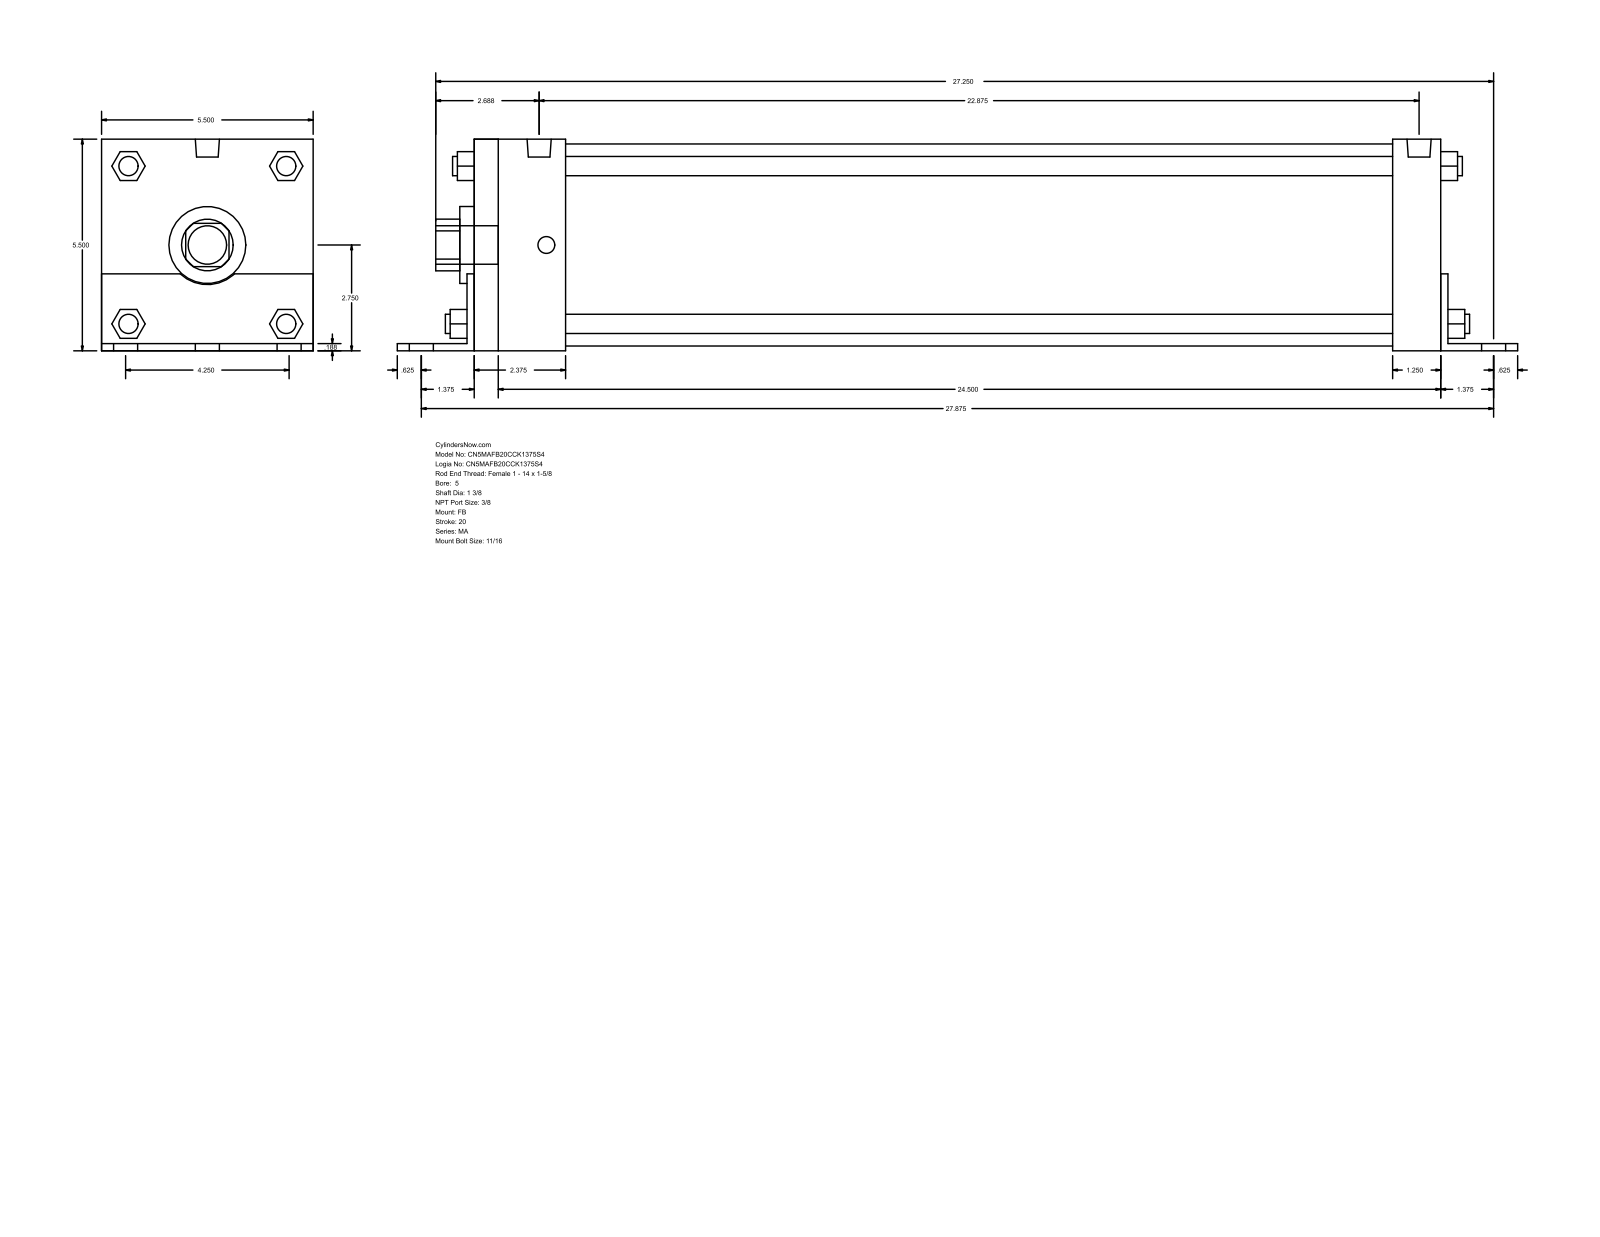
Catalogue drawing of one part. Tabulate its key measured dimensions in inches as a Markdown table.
| quantity | value |
| --- | --- |
| part name | MA_FB__0500_1.375 |
| STEP written by | GSSL Pune (CONFIG_CONTROL_DESIGN) |
| units | inches |
| bodies | 0 solids, 140 faces (105 planar, 35 cylindrical, 0 other) |
| overall size | 29.125 × 5.502 × 5.5 |
| round holes (diameter × count) | 1.375 × 1, 2 × 1, 5.25 × 1 |
| round bosses / shafts (diameter × count) | 0.687 × 6, 0.5 × 4, 0.437 × 4, 0.627 × 2, 1 × 1 |
| partial cylindrical surfaces (radius × count) | 0.672 × 1, 1.03 × 1 |
| main face-to-face distances | 5.5, 0.187, 5.502, 25.313, 0.185, 5.315, 25.125, 25.5, 1.25, 1.437 |
